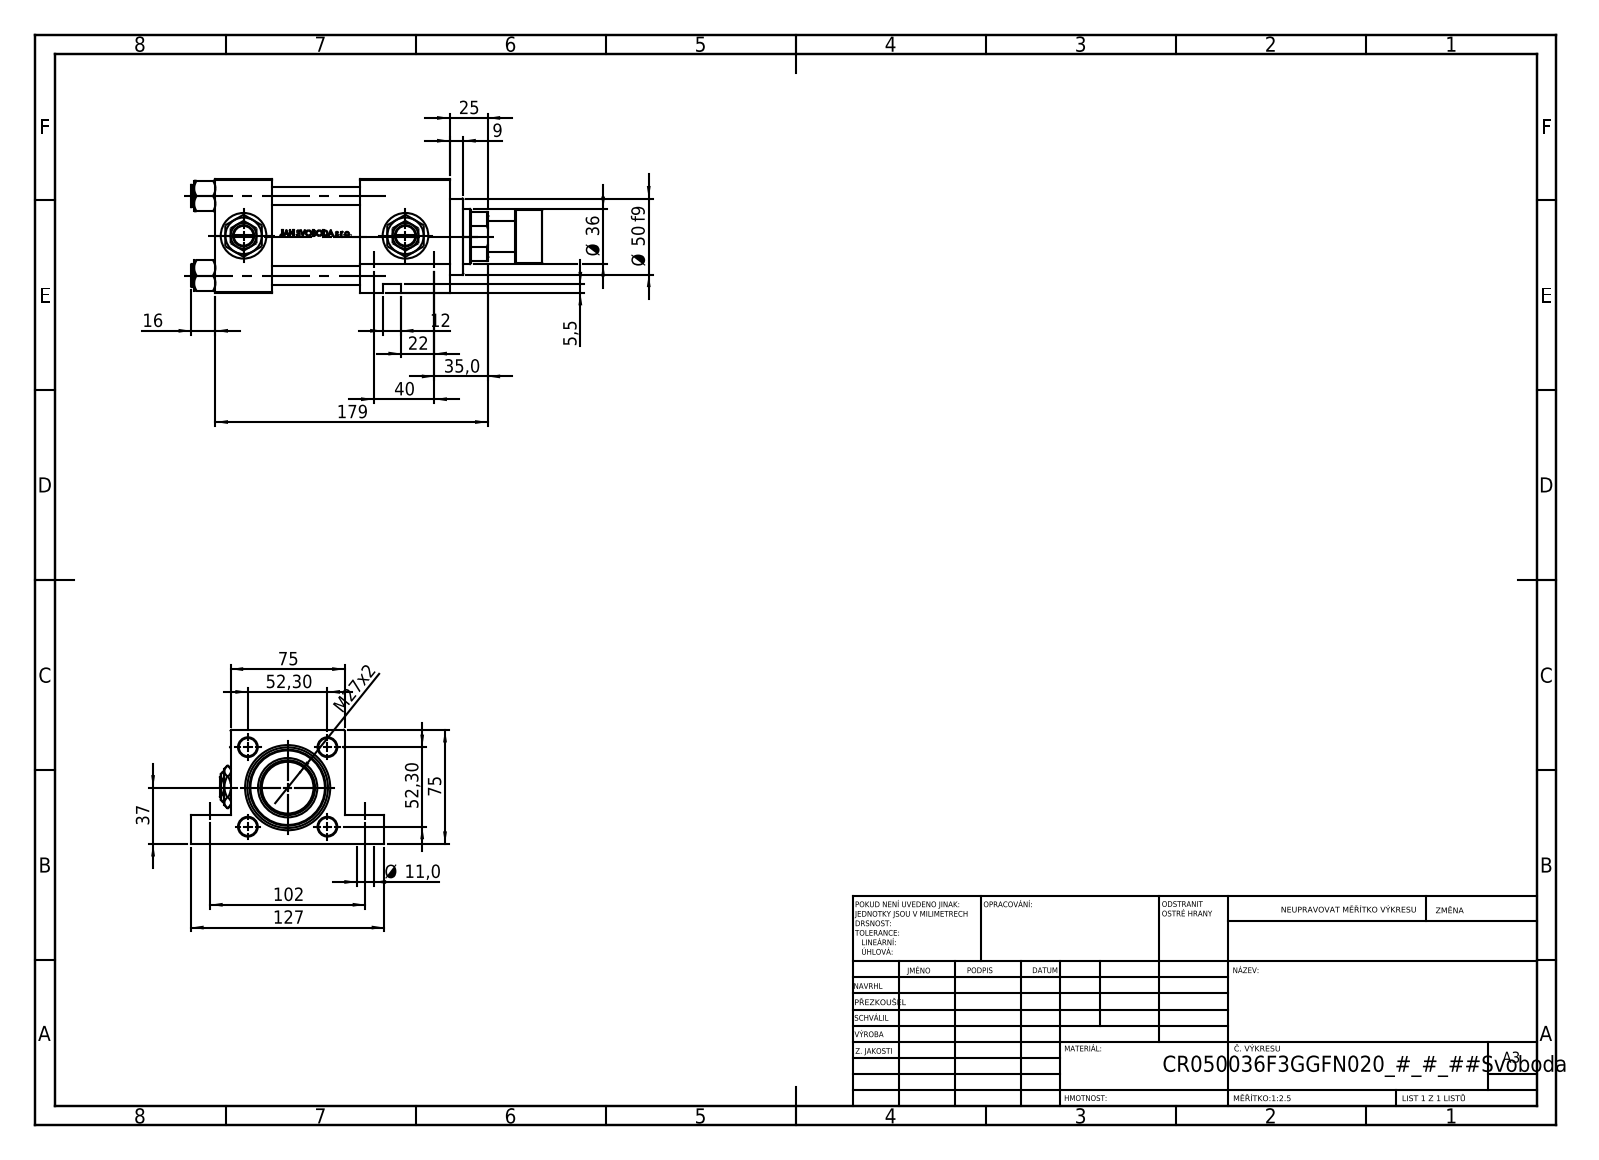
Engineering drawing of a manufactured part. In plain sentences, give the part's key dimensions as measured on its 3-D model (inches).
The part is named "V215CR_F_TYCINKA; V215CR_F_Body; Zatka_pro_OIL_PORT; V215CR_VCP_F (+3 more)". Its 3-D file was written by "SolidWorks 2019 (CONFIG_CONTROL_DESIGN)". It is 14 solids with 1216 faces: 488 planar, 140 cylindrical and 588 other. Overall it measures 9.094 by 5 by 2.953 inches. Its volume is 45.98 cubic inches and its surface area 270.5 square inches. Round holes: 4 of diameter 0.472, 4 of diameter 0.825, 4 of diameter 1.181, 3 of diameter 0.276, 2 of diameter 0.433, 2 of diameter 0.433, 1 of diameter 1.004, 1 of diameter 1.417, 1 of diameter 1.535, 1 of diameter 1.614, 1 of diameter 2.087. Round bosses or shafts: 4 of diameter 0.591, 1 of diameter 2.205, 1 of diameter 1.969, 1 of diameter 1.378, 1 of diameter 0.827. The main face-to-face distances are 2.953, 1.457, 2.283, 3.74, 2.323, 6.063, 4.606, 0.748, 2.205, 2.945. The hole center spacings are 2.059, 1.442, 1.47, 1.575, 2.032, 2.37, 2.912, 3.92.
